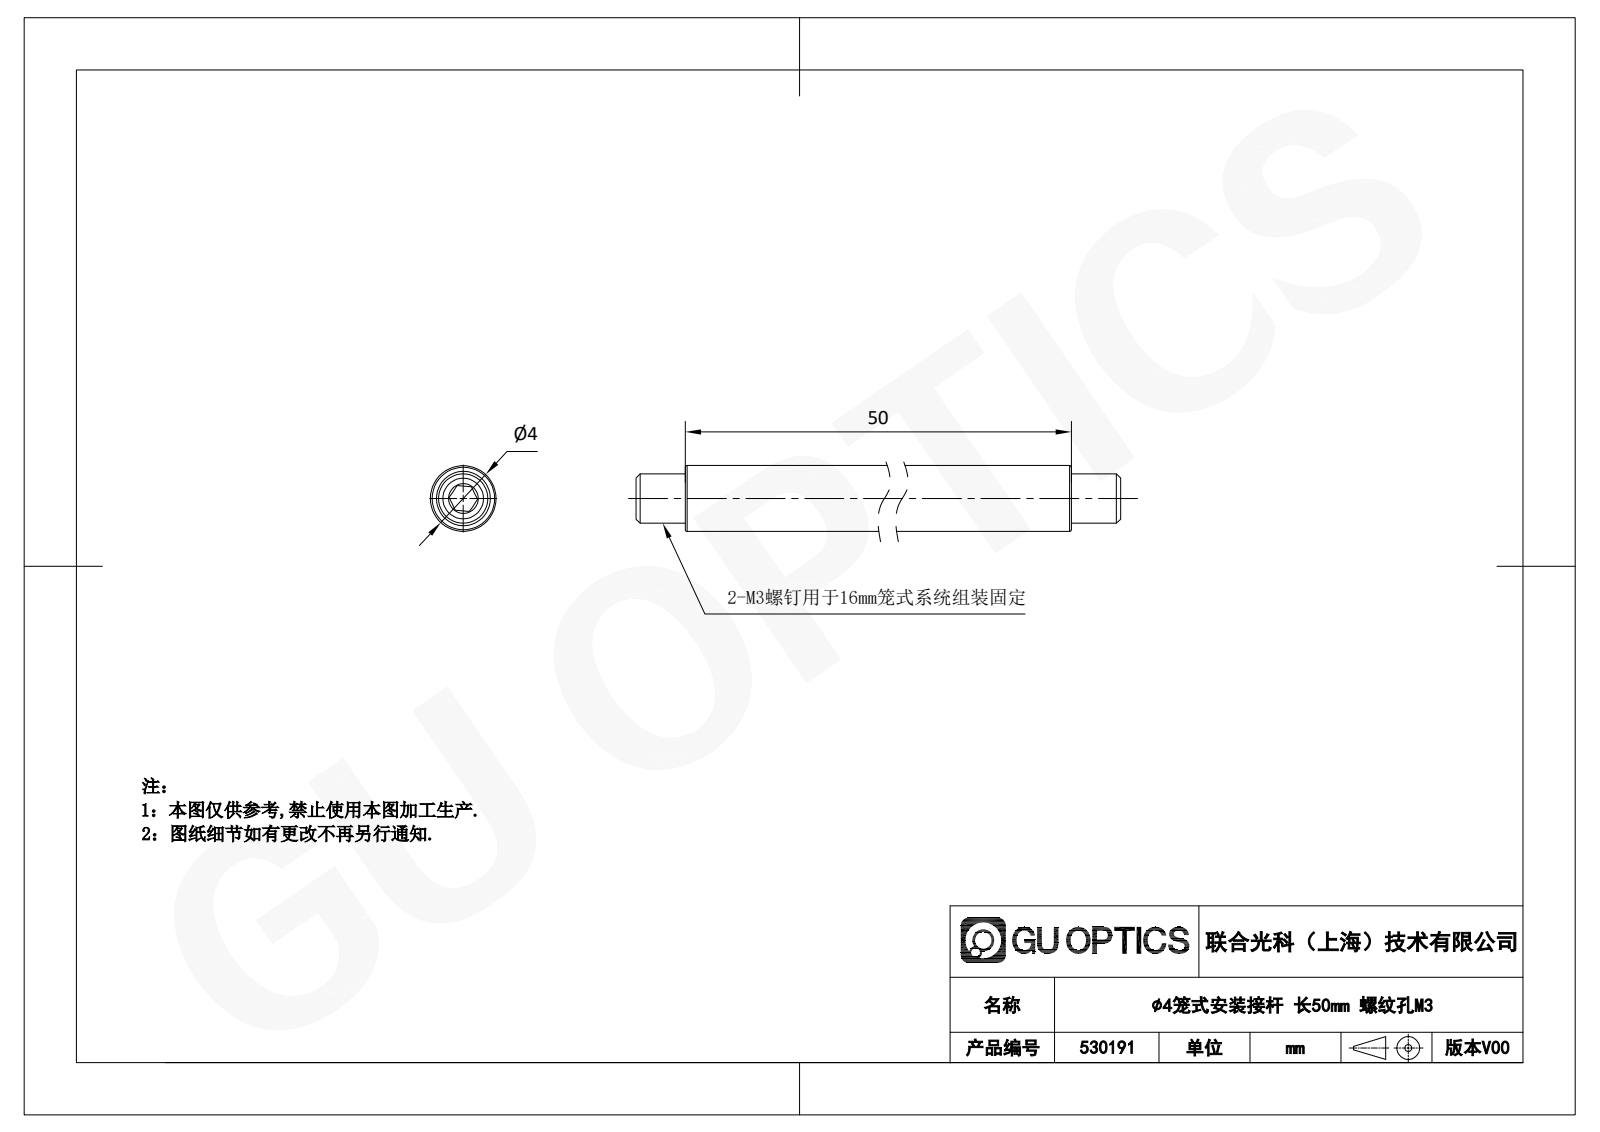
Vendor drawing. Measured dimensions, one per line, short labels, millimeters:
name: 530191
written by: SolidWorks 2020 (CONFIG_CONTROL_DESIGN)
unit: mm
bodies: 3 solids, 37 faces (20 planar, 5 cylindrical, 12 other)
size: 60 × 4 × 4
volume: 678 mm³; area: 918 mm²
holes: 1× ⌀2.5
bosses: 1× ⌀4, 1× ⌀3
face distances: 3, 47, 5, 8, 52, 55, 1.5, 50, 1, 59
